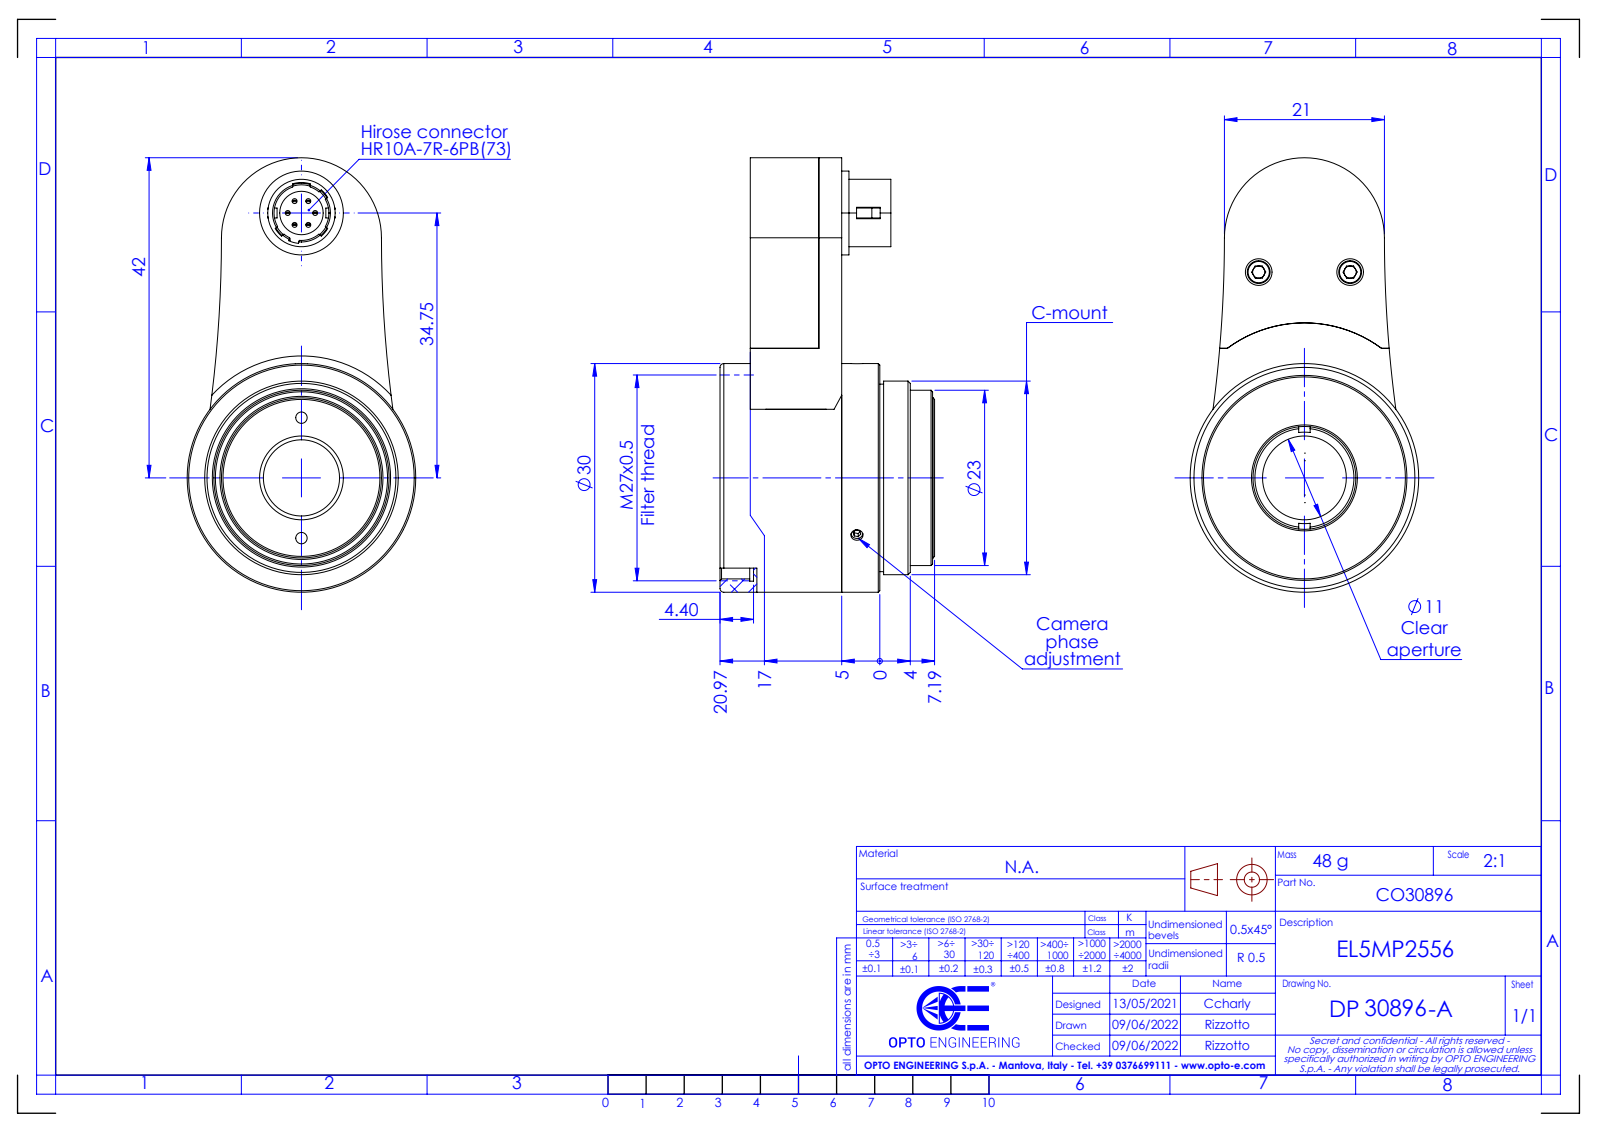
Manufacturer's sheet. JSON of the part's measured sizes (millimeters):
{"part_name": "DP30896-A_EL5MP2556", "step_written_by": "SolidWorks 2021 (CONFIG_CONTROL_DESIGN)", "units": "millimeters", "bodies": {"solids": 0, "faces": 220, "planar": 91, "cylindrical": 81, "other": 48}, "overall_size": [57, 30, 28.16], "round_holes": [[1.6, 3], [1.5, 2], [3.5, 2], [7.4, 1], [10, 1], [11, 1], [13.5, 1], [26.5, 1], [27.1, 1]], "round_bosses_or_shafts": [[1.2, 2], [30, 1], [25.4, 1], [24.6, 1], [23, 1], [21, 1], [11, 1], [8.85, 1]], "partial_cylinders_radius": [[0.4, 2], [169.5, 2], [3.6, 1], [3.9, 1], [4, 1], [10.5, 1], [17, 1]], "face_to_face_distances": [12, 0.43, 11.57, 24.19, 23.76, 12.19, 17, 16.57, 5, 7.19], "hole_center_spacings": [7.9, 9.8, 20.02, 27.66, 35.41, 12, 15.8, 26.85]}
